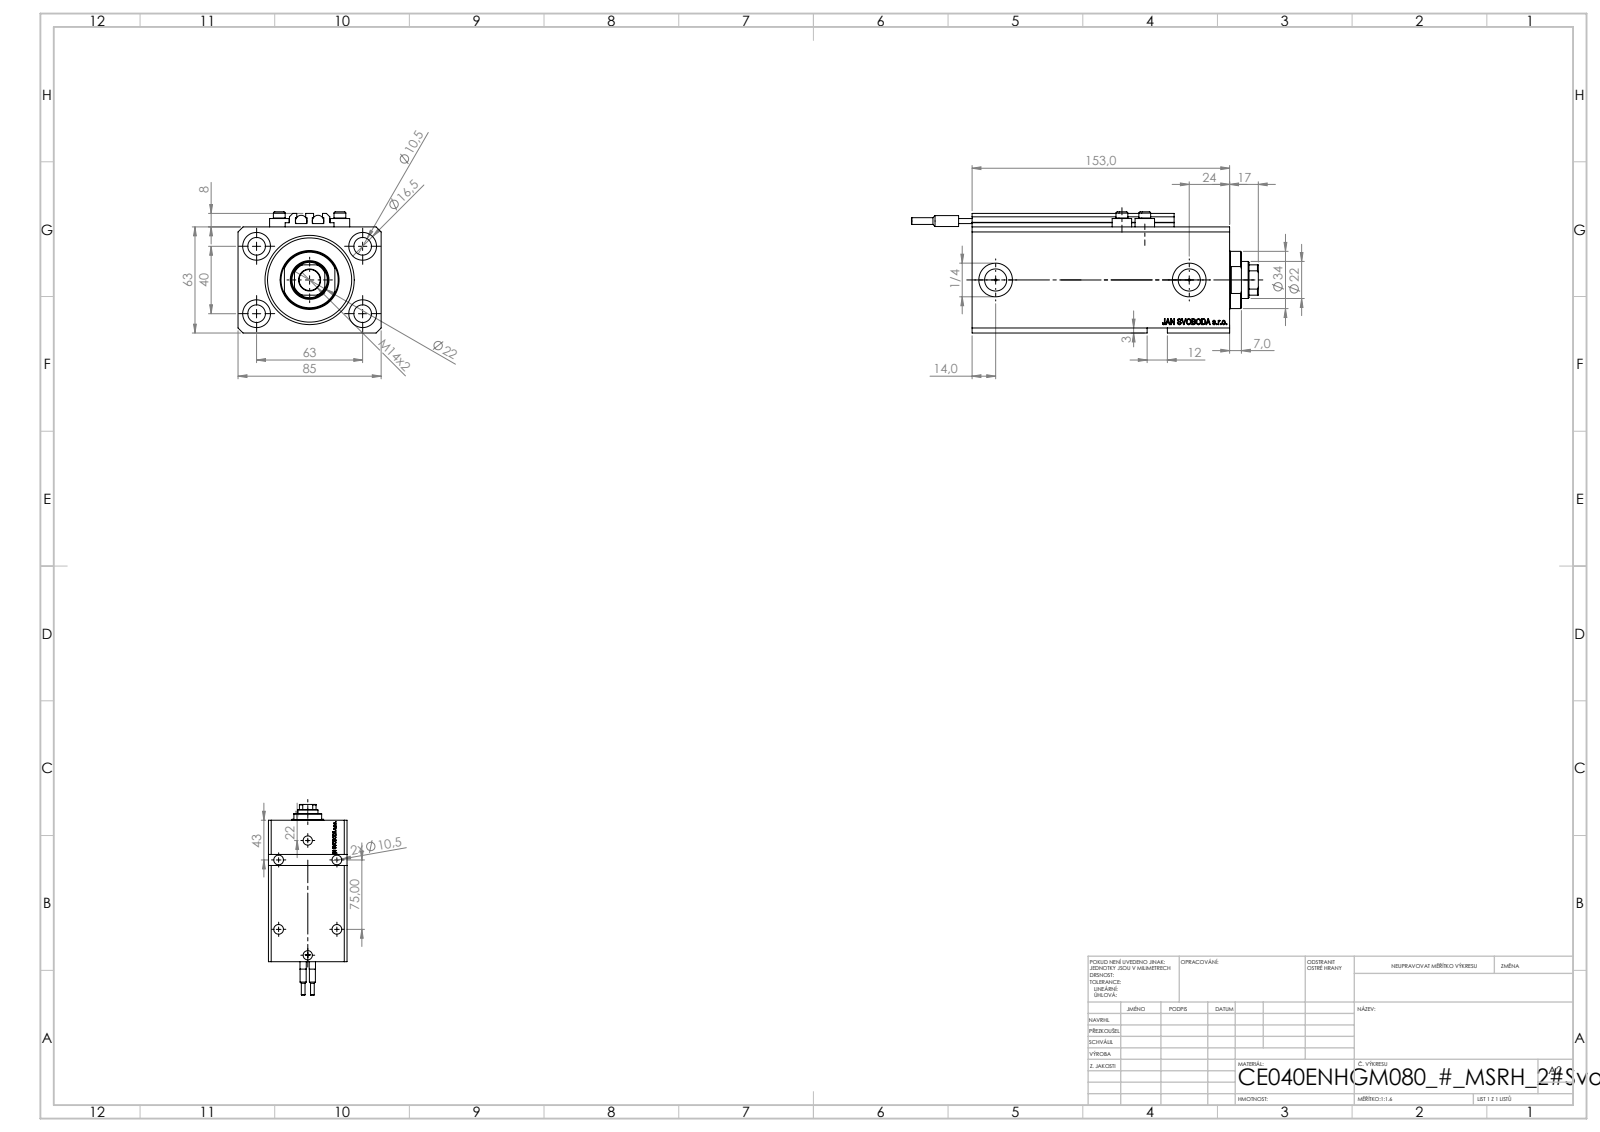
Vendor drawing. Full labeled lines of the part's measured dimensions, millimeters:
Part name (STEP PRODUCT): SWITCH_V250CE; V250CE_VC_E; ALLEN BOLT V250CE; V250CE_E_Body (+1 more)
STEP written by: SolidWorks 2019 (CONFIG_CONTROL_DESIGN)
Units: millimetres
Bodies: 10 solids, 1159 faces (567 planar, 158 cylindrical, 434 other)
Overall size (bounding box): 206 × 85 × 72
Volume: 687 421 mm³ · Surface area: 143 572 mm²
Round holes (diameter × count): ⌀10.5 ×8, ⌀1.25 ×4, ⌀4 ×4, ⌀16.5 ×4, ⌀10 ×2, ⌀13.16 ×2, ⌀20 ×2, ⌀12.5 ×1, ⌀22 ×1, ⌀40 ×1, ⌀53 ×1
Round bosses / shafts (diameter × count): ⌀11.6 ×4, ⌀7 ×4, ⌀6.8 ×2, ⌀6.5 ×2, ⌀4 ×2, ⌀34 ×1
Partial cylindrical surfaces — rounded edges, fillets, slot ends (radius × count): R0.2 ×10, R10.5 ×1
Main face-to-face distances: 63, 85, 153, 17, 136, 3, 65, 11.4, 124.6, 141.6
Hole centre spacings: 37.31, 63, 13.6, 15.4, 24.96, 33.62, 36, 37.86
